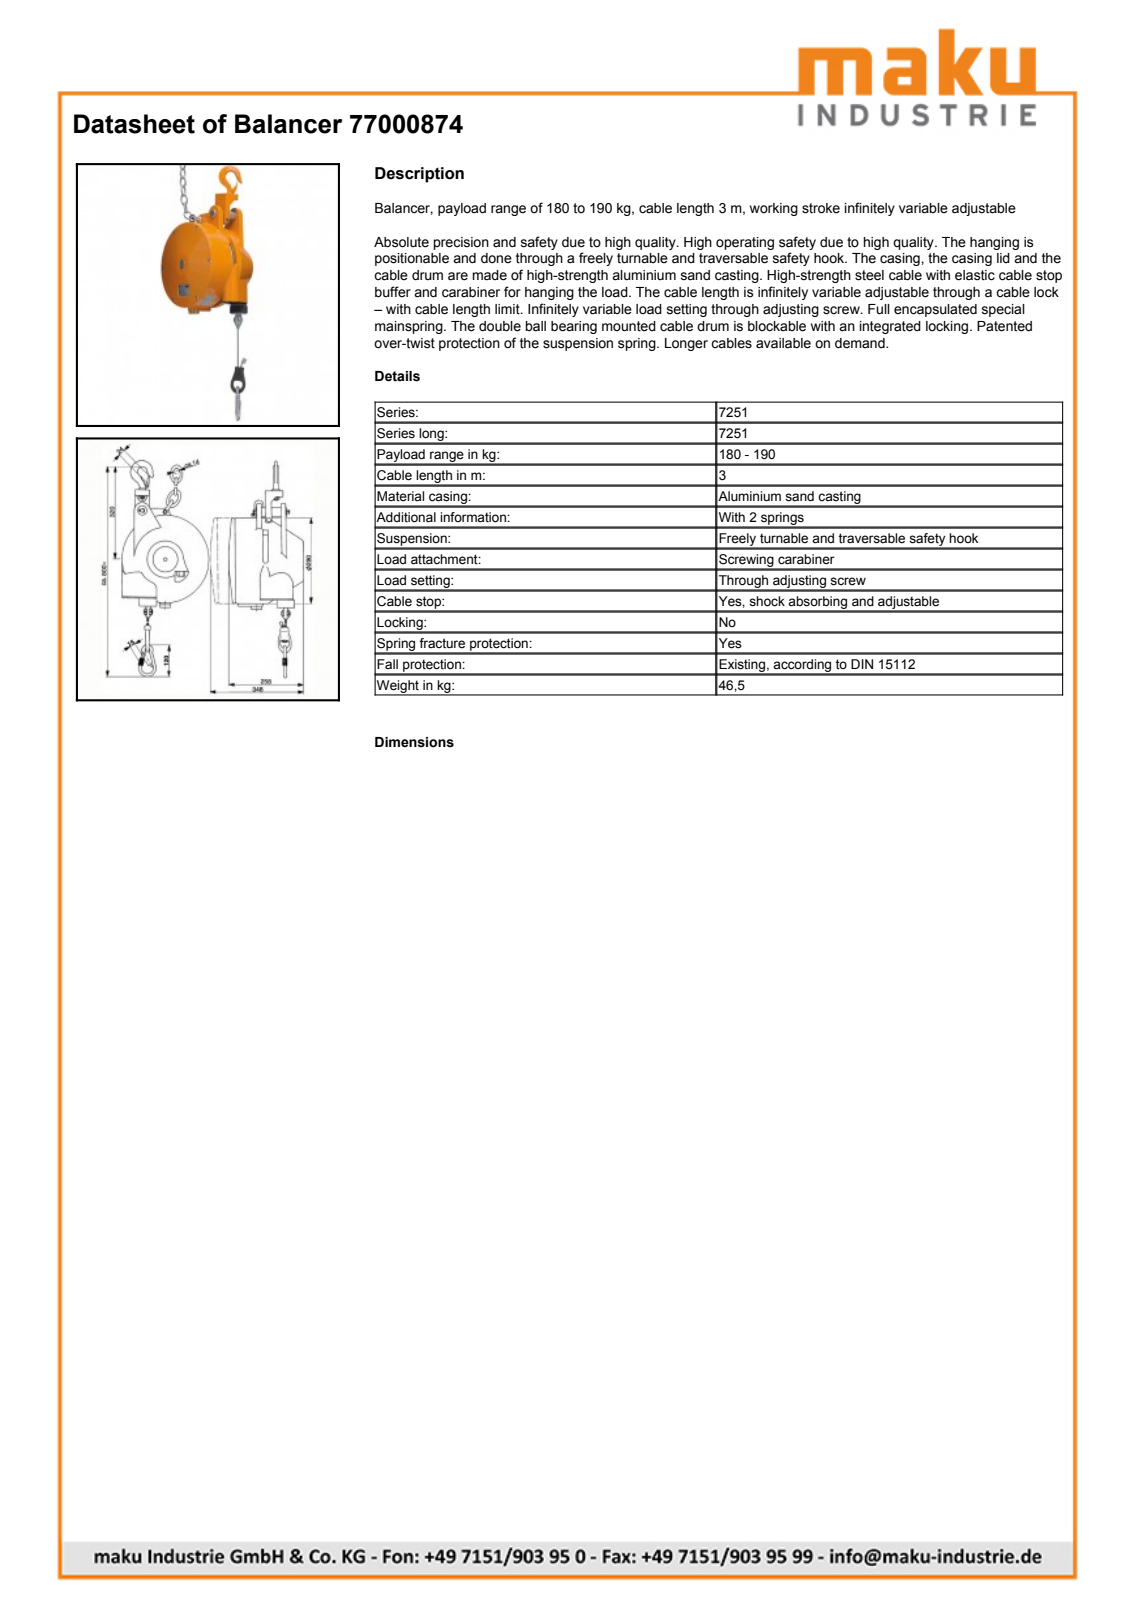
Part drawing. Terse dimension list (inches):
name: 002-7251080001-AE
written by: Autodesk Inventor 2014 (CONFIG_CONTROL_DESIGN)
unit: in
bodies: 14 solids, 1895 faces (740 planar, 370 cylindrical, 785 other)
size: 34.269 × 12.79 × 10.087
volume: 839.1 in³; area: 842.4 in²
holes: 3× ⌀0.256, 2× ⌀0.354, 1× ⌀0.138, 1× ⌀0.161, 1× ⌀0.177, 1× ⌀0.197, 1× ⌀0.224, 1× ⌀0.236, 1× ⌀0.26, 1× ⌀0.262, 1× ⌀0.394, 1× ⌀0.472
bosses: 6× ⌀0.63, 5× ⌀0.433, 5× ⌀0.197, 5× ⌀0.039, 4× ⌀0.236, 3× ⌀0.394, 2× ⌀0.945, 2× ⌀0.35
rounds: 35× R0.079, 33× R0.118, 32× R0.006, 31× R0.197, 24× R0.039, 12× R0.051, 7× R0.098, 6× R0.157
face distances: 0.039, 2.728, 1.704, 2.689, 0.985, 1.024, 1.743, 2.767, 3.504, 10.079
hole spacings: 6.378, 0.646, 0.683, 0.709, 1.396, 1.634, 1.643, 2.735
